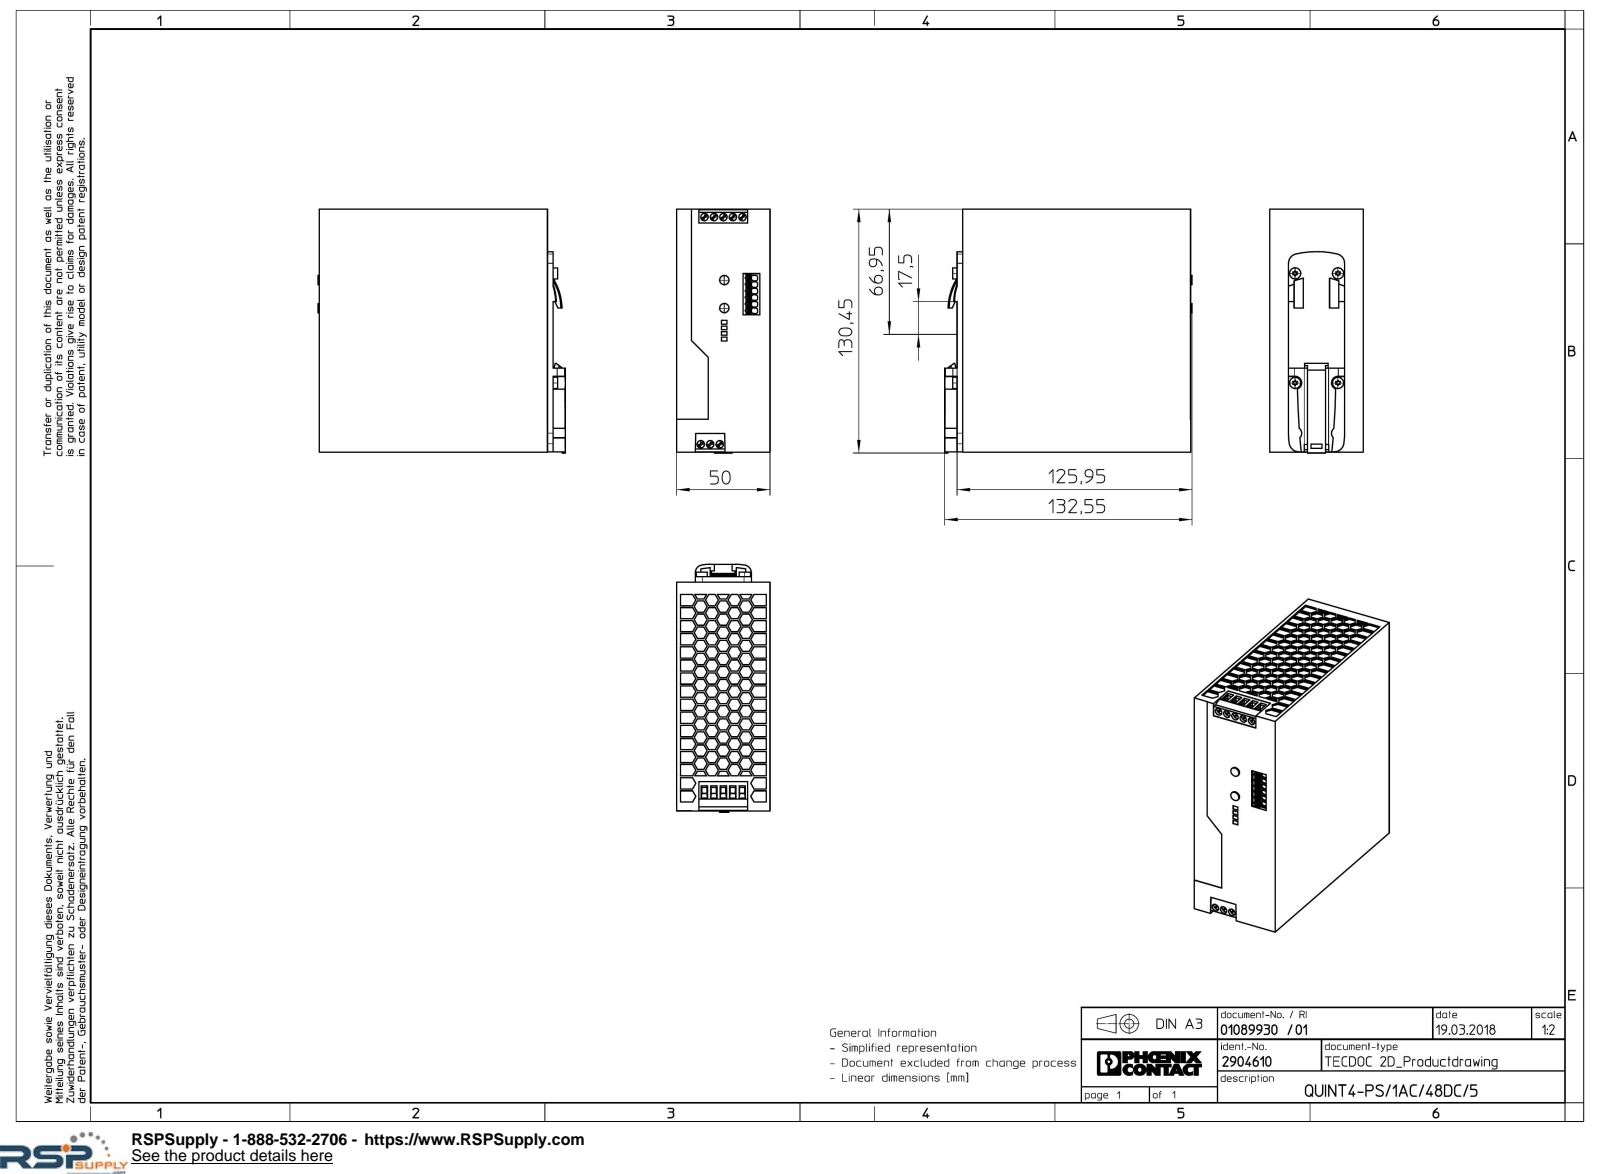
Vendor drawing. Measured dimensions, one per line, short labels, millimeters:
name: QUINT4_PS_1AC_48DC_5-select
written by: Creo Elements/Direct Modeling 20.1A 29-Sep-2018 (C) Parametric Technology GmbH (AUTOMOTIVE_DESIGN)
unit: mm
bodies: 1 solid, 1931 faces (1796 planar, 119 cylindrical, 16 other)
size: 132.55 × 130.45 × 50.06
volume: 804 095 mm³; area: 64 169 mm²
holes: 8× ⌀4
bosses: 4× ⌀6, 2× ⌀5
rounds: 48× R0.1, 12× R0.97, 6× R0.57, 6× R0.6, 4× R3.5, 4× R5, 2× R4, 2× R30
face distances: 50.06, 0.8, 129.2, 128.4, 122.25, 130, 3, 125.25, 125.1, 122.1
hole spacings: 5.08, 10.16, 121.49, 121.67, 122.08, 15.24, 121.51, 122.68
